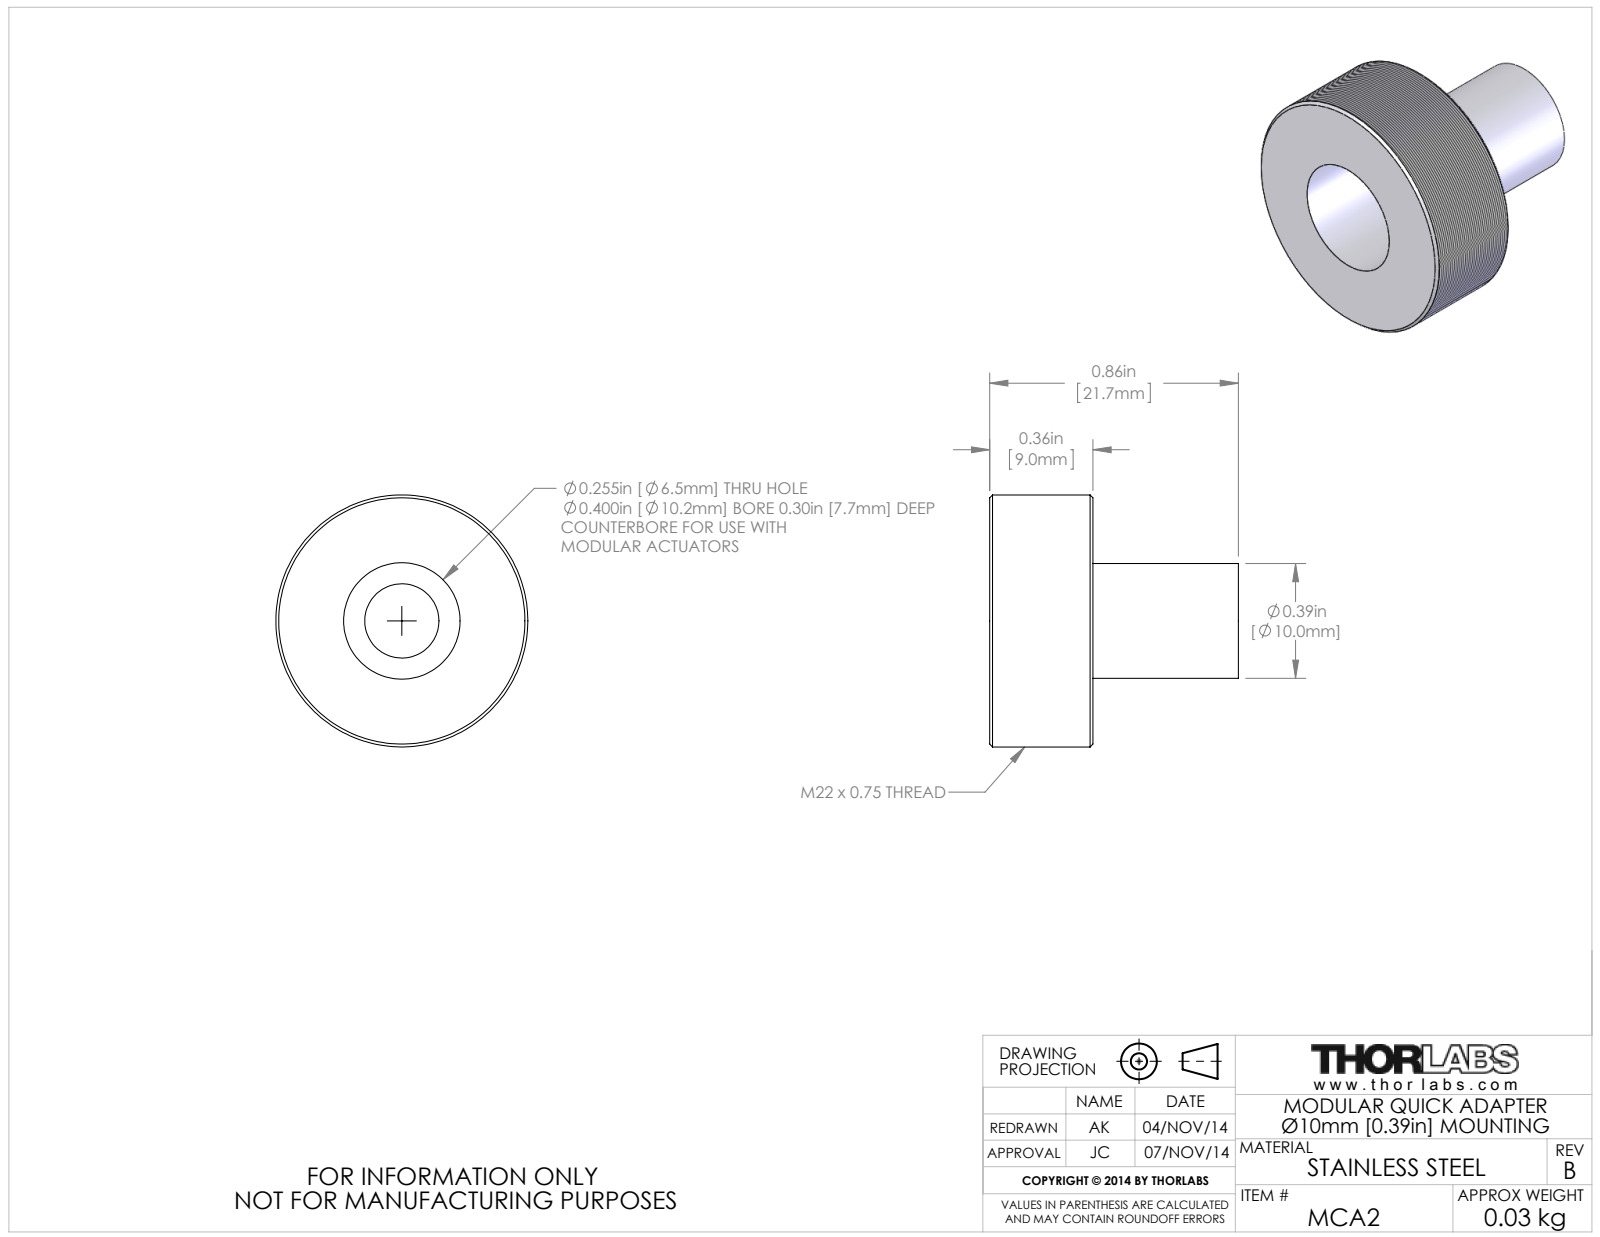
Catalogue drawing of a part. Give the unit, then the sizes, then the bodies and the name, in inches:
Units: inches
Overall size (bounding box): 0.866 × 0.866 × 0.855
Round holes (diameter × count): ⌀0.255 ×1, ⌀0.4 ×1
Round bosses / shafts (diameter × count): ⌀0.866 ×1, ⌀0.394 ×1
Main face-to-face distances: 0.355, 0.855, 0.5
Bodies: 0 solids, 15 faces (3 planar, 8 cylindrical, 4 other)
Part name (STEP PRODUCT): 12613-E0W
STEP written by: SolidWorks 2014 (AUTOMOTIVE_DESIGN)
